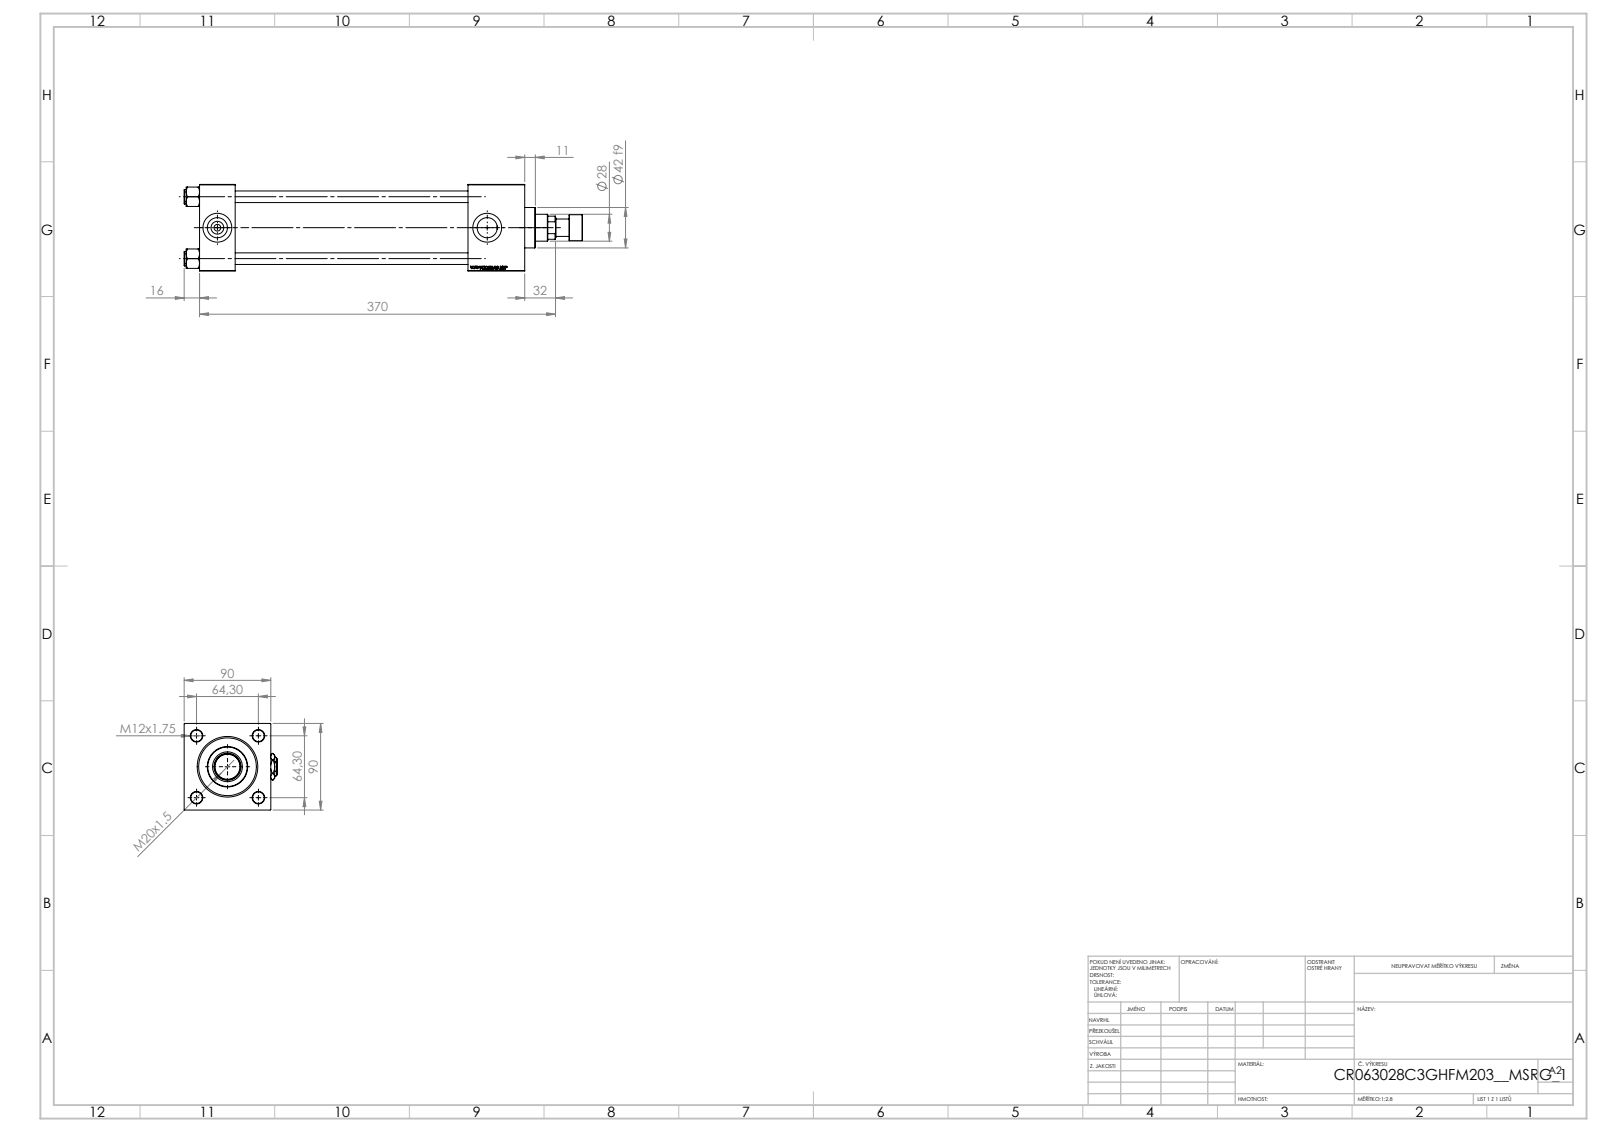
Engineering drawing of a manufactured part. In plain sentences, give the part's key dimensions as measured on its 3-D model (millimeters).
The part is named "V215CR_C_TYCINKA; Zatka_pro_OIL_PORT; V215CR_C_Body; V215CR_VCP_C (+3 more)". Its 3-D file was written by "SolidWorks 2019 (CONFIG_CONTROL_DESIGN)". It is 14 solids with 1264 faces: 578 planar, 102 cylindrical and 584 other. Overall it measures 414 by 97 by 90 millimeters. Its volume is 1 261 000 cubic millimeters and its surface area 306 754 square millimeters. Round holes: 4 of diameter 12, 2 of diameter 7, 2 of diameter 20.96, 2 of diameter 30, 1 of diameter 18.5, 1 of diameter 28, 1 of diameter 31, 1 of diameter 50, 1 of diameter 60, 1 of diameter 63. Round bosses or shafts: 4 of diameter 15, 1 of diameter 69, 1 of diameter 42, 1 of diameter 27, 1 of diameter 18. The main face-to-face distances are 90, 37, 301, 338, 59, 279, 242, 309.3, 272.3, 30.3. The hole center spacings are 45.47, 64.3, 90.93, 280.5.
